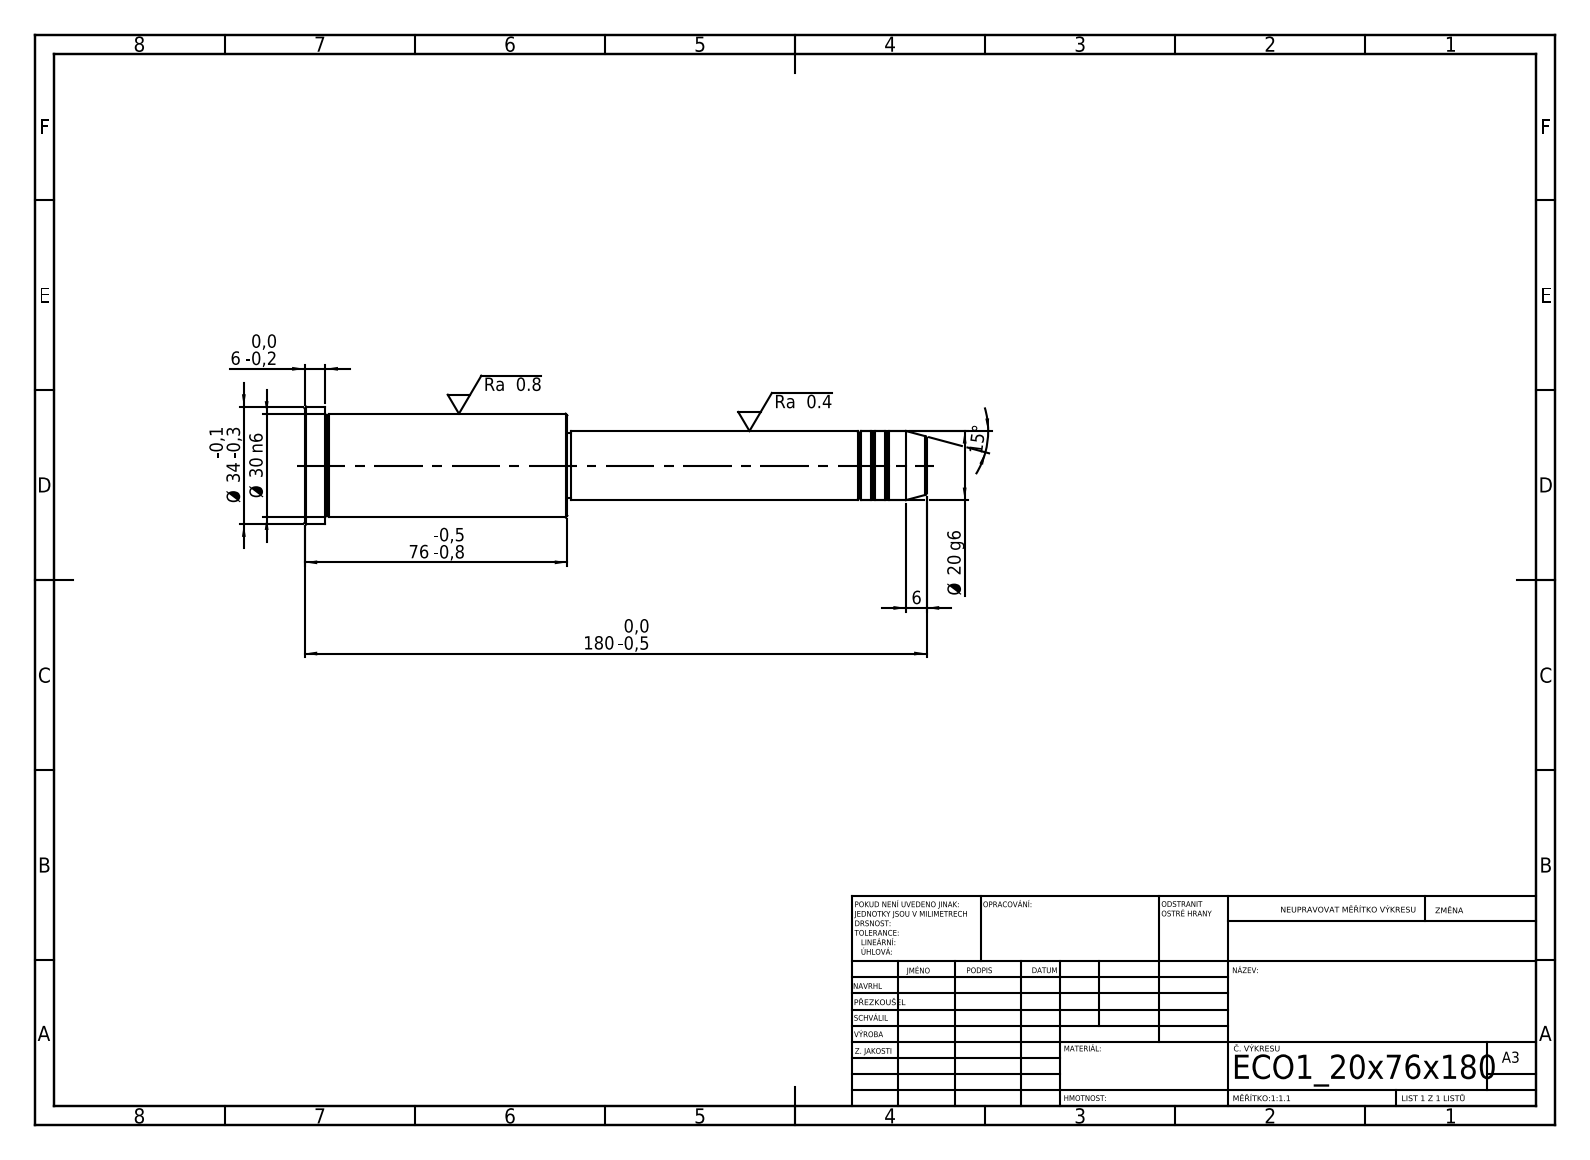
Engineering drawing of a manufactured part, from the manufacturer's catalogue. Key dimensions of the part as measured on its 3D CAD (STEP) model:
STEP written by: SolidWorks 2019 (CONFIG_CONTROL_DESIGN)
Units: millimetres
Bodies: 1 solid, 43 faces (5 planar, 14 cylindrical, 24 other)
Overall size (bounding box): 180 × 34 × 34
Volume: 87 147 mm³ · Surface area: 15 619 mm²
Round bosses / shafts (diameter × count): ⌀34 ×1, ⌀30 ×1, ⌀20 ×1, ⌀19 ×1
Main face-to-face distances: 76, 104, 180, 174, 70, 6, 103, 1, 71, 77
